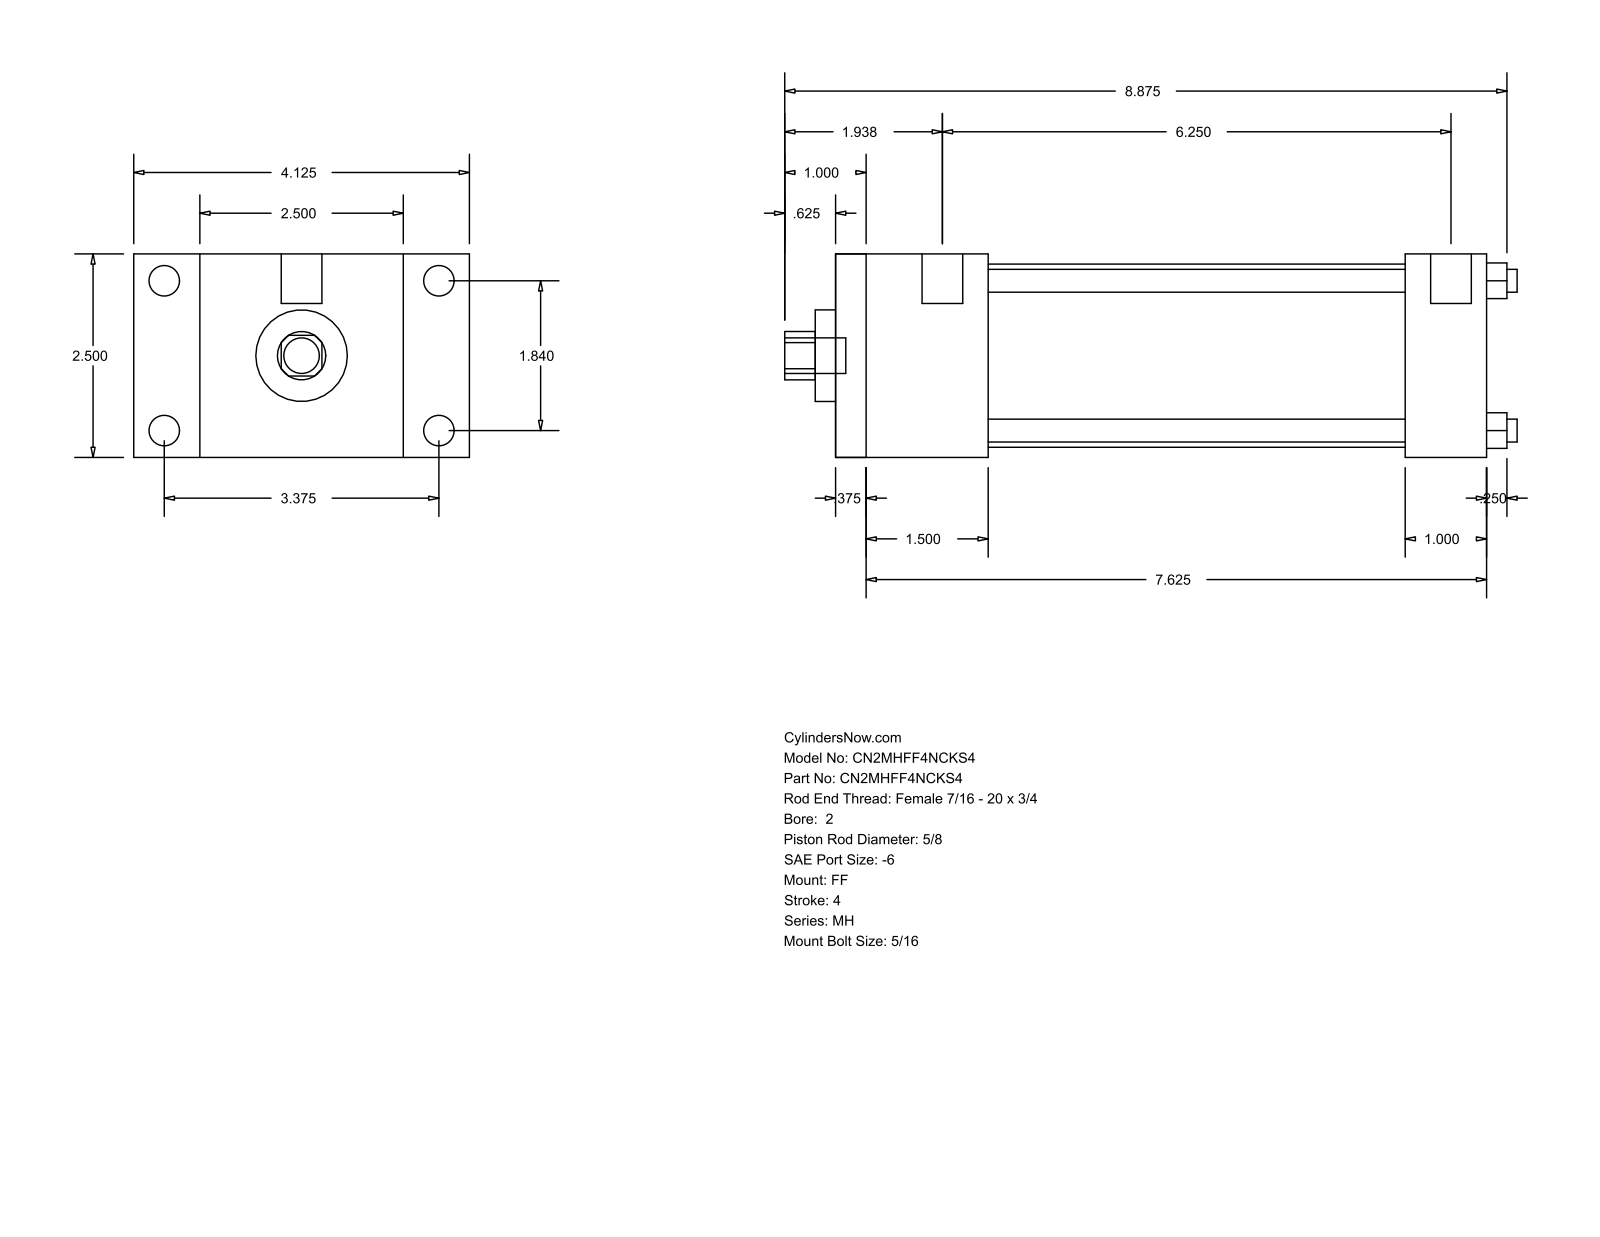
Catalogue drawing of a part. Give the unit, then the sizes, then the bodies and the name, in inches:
Units: inches
Overall size (bounding box): 9 × 4.125 × 2.5
Round holes (diameter × count): ⌀0.281 ×4, ⌀0.625 ×1, ⌀1.125 ×1, ⌀2.25 ×1
Round bosses / shafts (diameter × count): ⌀0.375 ×4, ⌀0.219 ×4, ⌀0.5 ×2, ⌀0.437 ×1
Partial cylindrical surfaces — rounded edges, fillets, slot ends (radius × count): R0.297 ×1
Main face-to-face distances: 2.5, 8, 0.375, 7.625, 1.5, 1.875, 7, 6.625, 5.125, 6.125
Hole centre spacings: 1.301, 1.84, 2.602
Bodies: 0 solids, 92 faces (64 planar, 28 cylindrical, 0 other)
Part name (STEP PRODUCT): MH_FF__0200_0.625
STEP written by: GSSL Pune (CONFIG_CONTROL_DESIGN)
